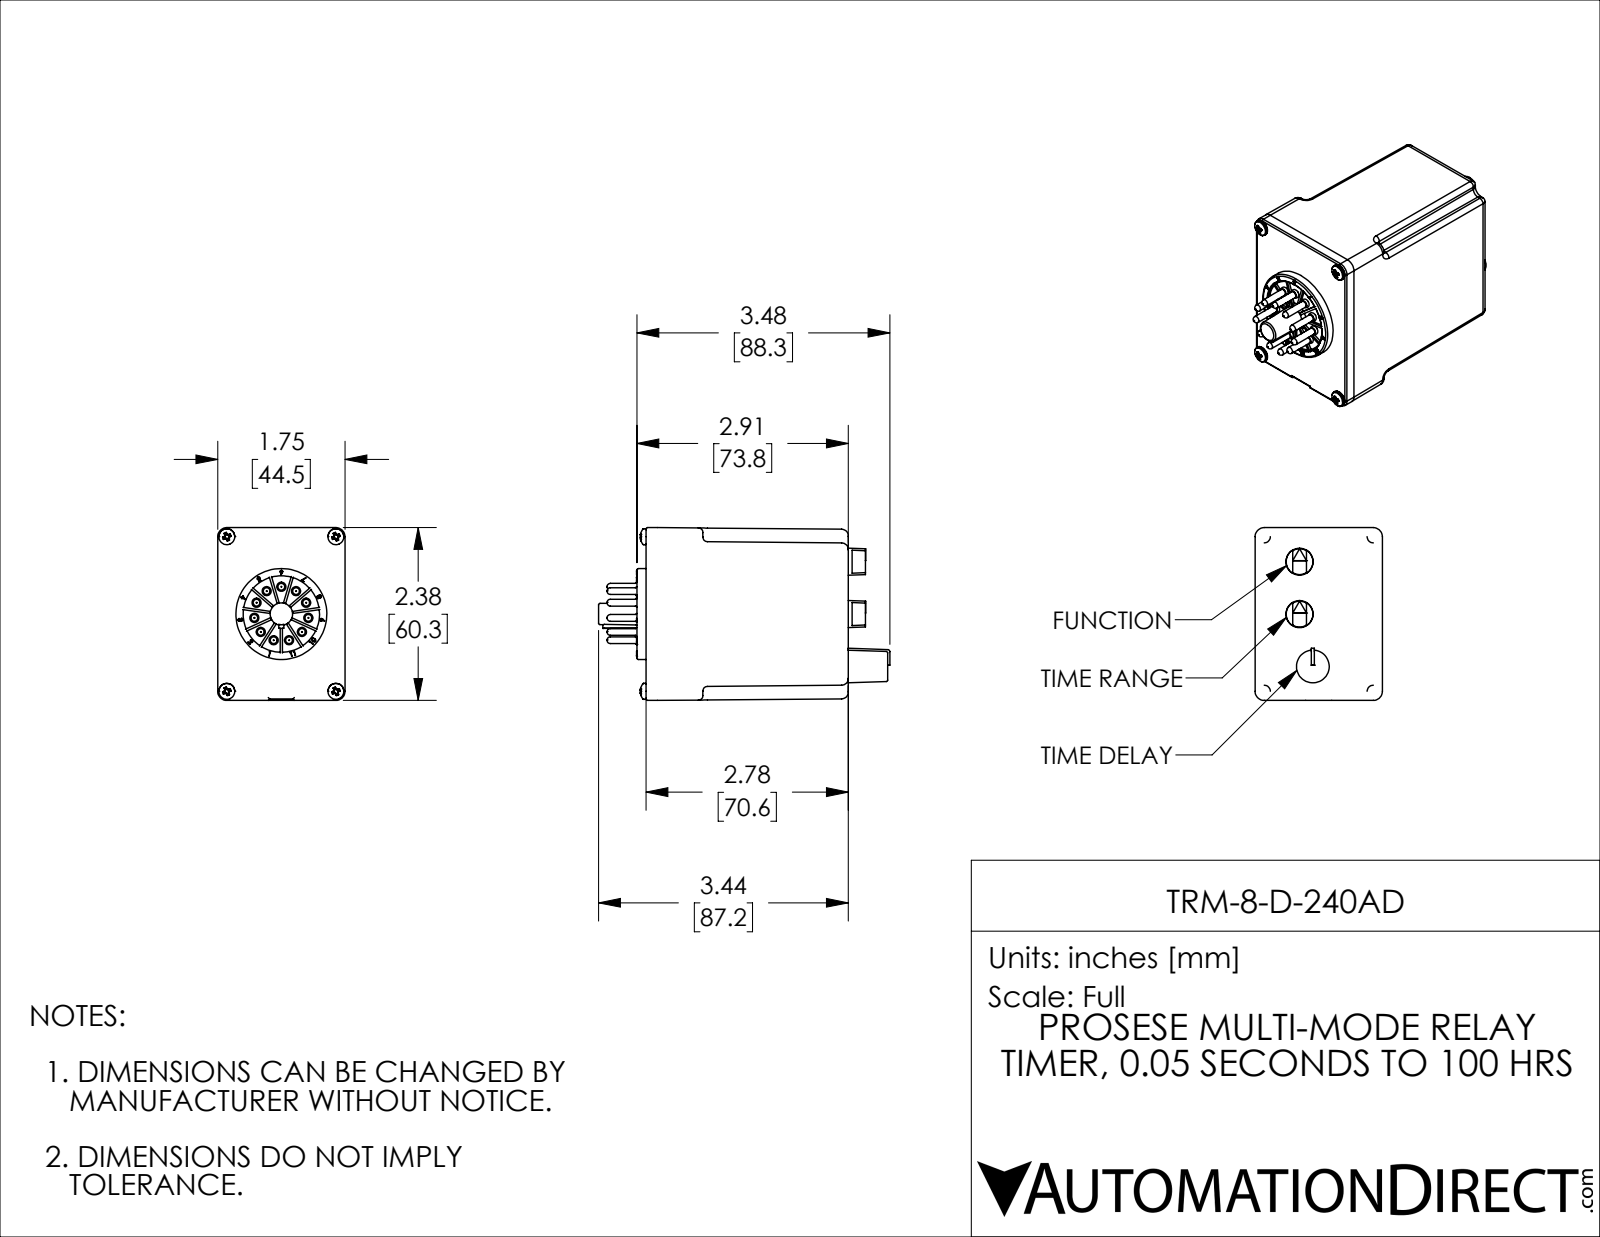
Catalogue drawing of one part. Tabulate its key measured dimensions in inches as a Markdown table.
| quantity | value |
| --- | --- |
| part name | TRM-8-D-240AD |
| STEP written by | SolidWorks 2024 (CONFIG_CONTROL_DESIGN) |
| units | inches |
| bodies | 4 solids, 1086 faces (382 planar, 301 cylindrical, 403 other) |
| overall size | 4.005 × 2.375 × 1.75 |
| volume | 11.08 in³ |
| surface area | 66.98 in² |
| round holes (diameter × count) | 0.01 × 11, 0.097 × 11, 0.075 × 10, 0.125 × 4, 0.075 × 1, 1.05 × 1 |
| round bosses / shafts (diameter × count) | 0.093 × 11, 0.219 × 4, 1.25 × 1 |
| partial cylindrical surfaces (radius × count) | 0.063 × 18, 0.02 × 11, 0.015 × 8, 0.02 × 8, 0.094 × 8, 0.125 × 4, 0.063 × 2, 0.028 × 1 |
| main face-to-face distances | 0.063, 1.58, 2.781, 2.206, 0.125, 0.085, 1.665, 2.875, 0.094, 0.125 |
| hole center spacings | 0.742, 0.405, 0.567, 0.375, 0.211, 0.211, 0.375, 1.301 |
